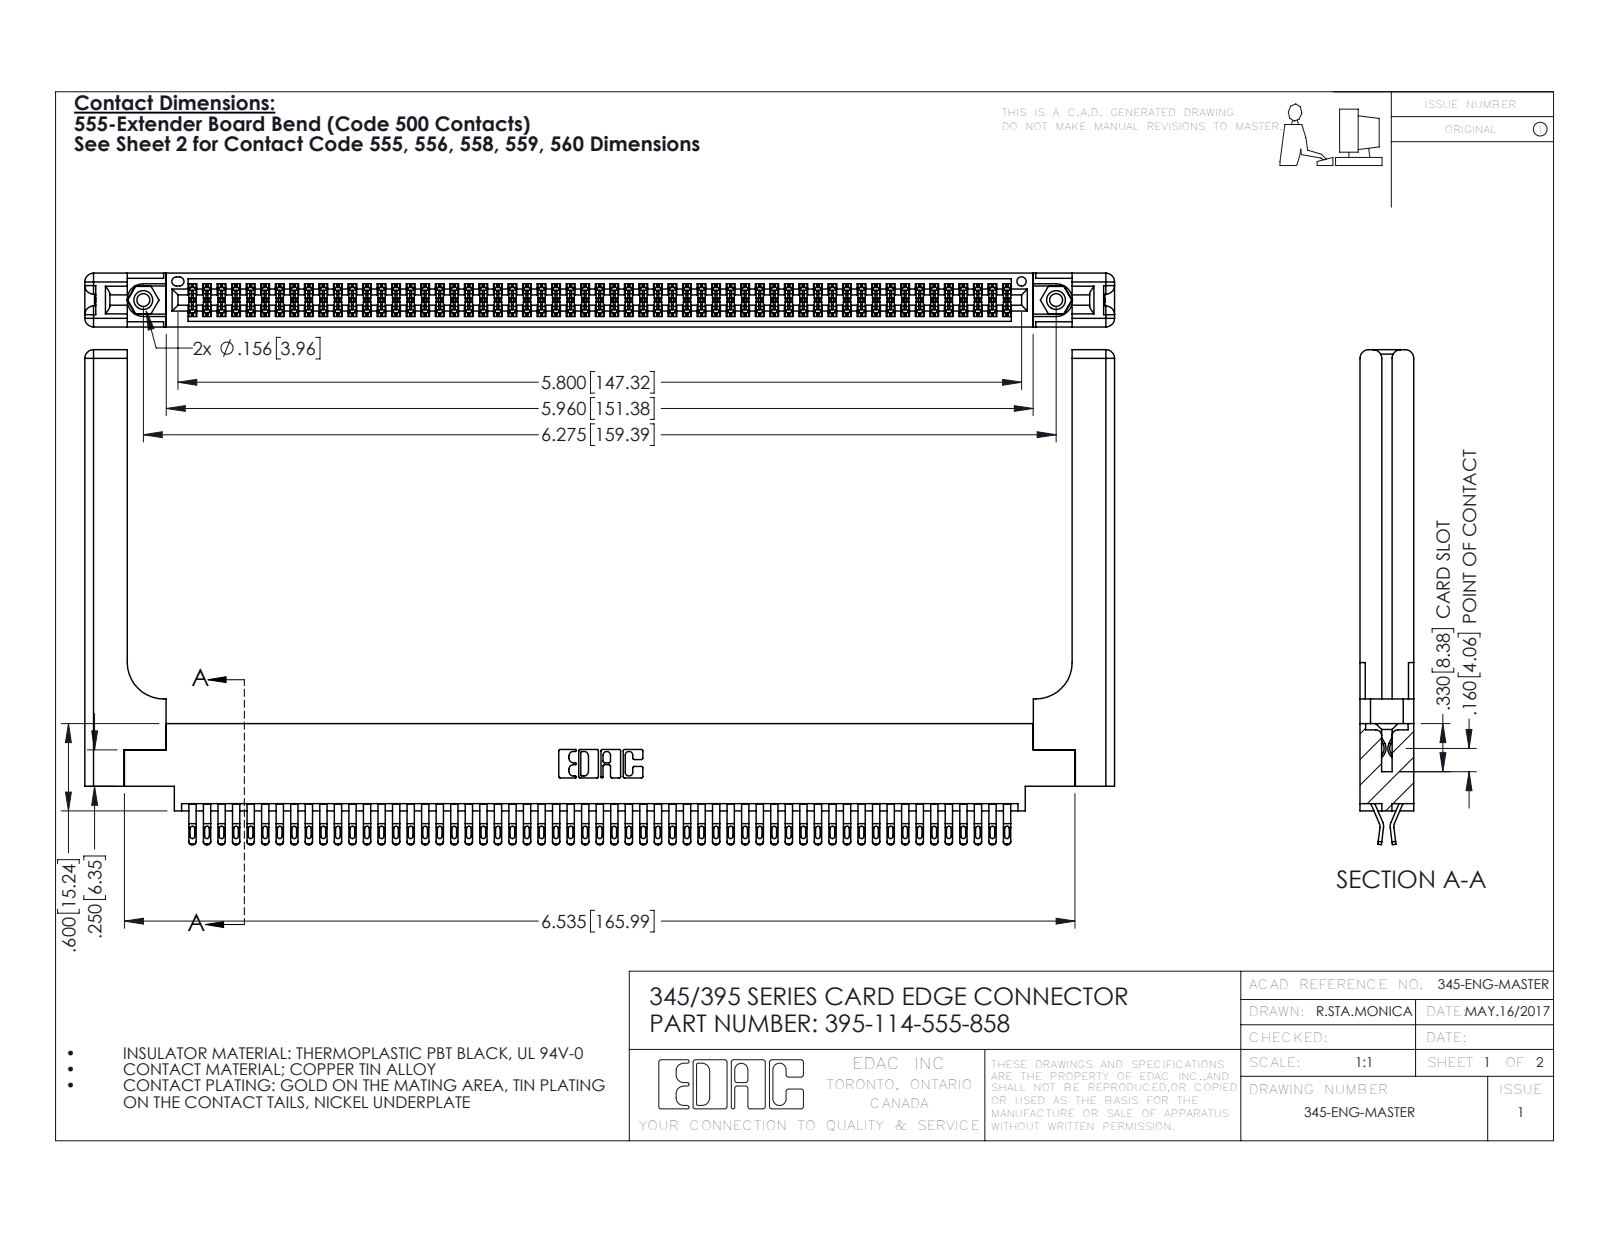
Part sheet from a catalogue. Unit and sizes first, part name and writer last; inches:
Units: inches
Overall size (bounding box): 7.079 × 3.402 × 0.37
Round holes (diameter × count): ⌀0.089 ×2, ⌀0.125 ×2, ⌀0.156 ×2, ⌀0.064 ×1
Round bosses / shafts (diameter × count): ⌀0.155 ×2
Partial cylindrical surfaces — rounded edges, fillets, slot ends (radius × count): R0.016 ×285, R0.02 ×228, R0.006 ×171, R0.01 ×22, R0.06 ×16, R0.007 ×6, R0.031 ×6, R0.026 ×3
Main face-to-face distances: 0.072, 0.37, 0.298, 0.025, 0.098, 0.272, 0.2, 0.225, 0.175, 0.148
Hole centre spacings: 0.27, 6.039, 6.275
Volume: 1.605 in³ · Surface area: 51.13 in²
Bodies: 119 solids, 6770 faces (3766 planar, 2944 cylindrical, 60 other)
Part name (STEP PRODUCT): 345 Part_0.170 Offset - 0.156 Dia-TH; 345-250-001_345-250-001-102; 395-114-555-858; 345-220-058_345-220-058 (+1 more)
STEP written by: SolidWorks 2016 (CONFIG_CONTROL_DESIGN)
